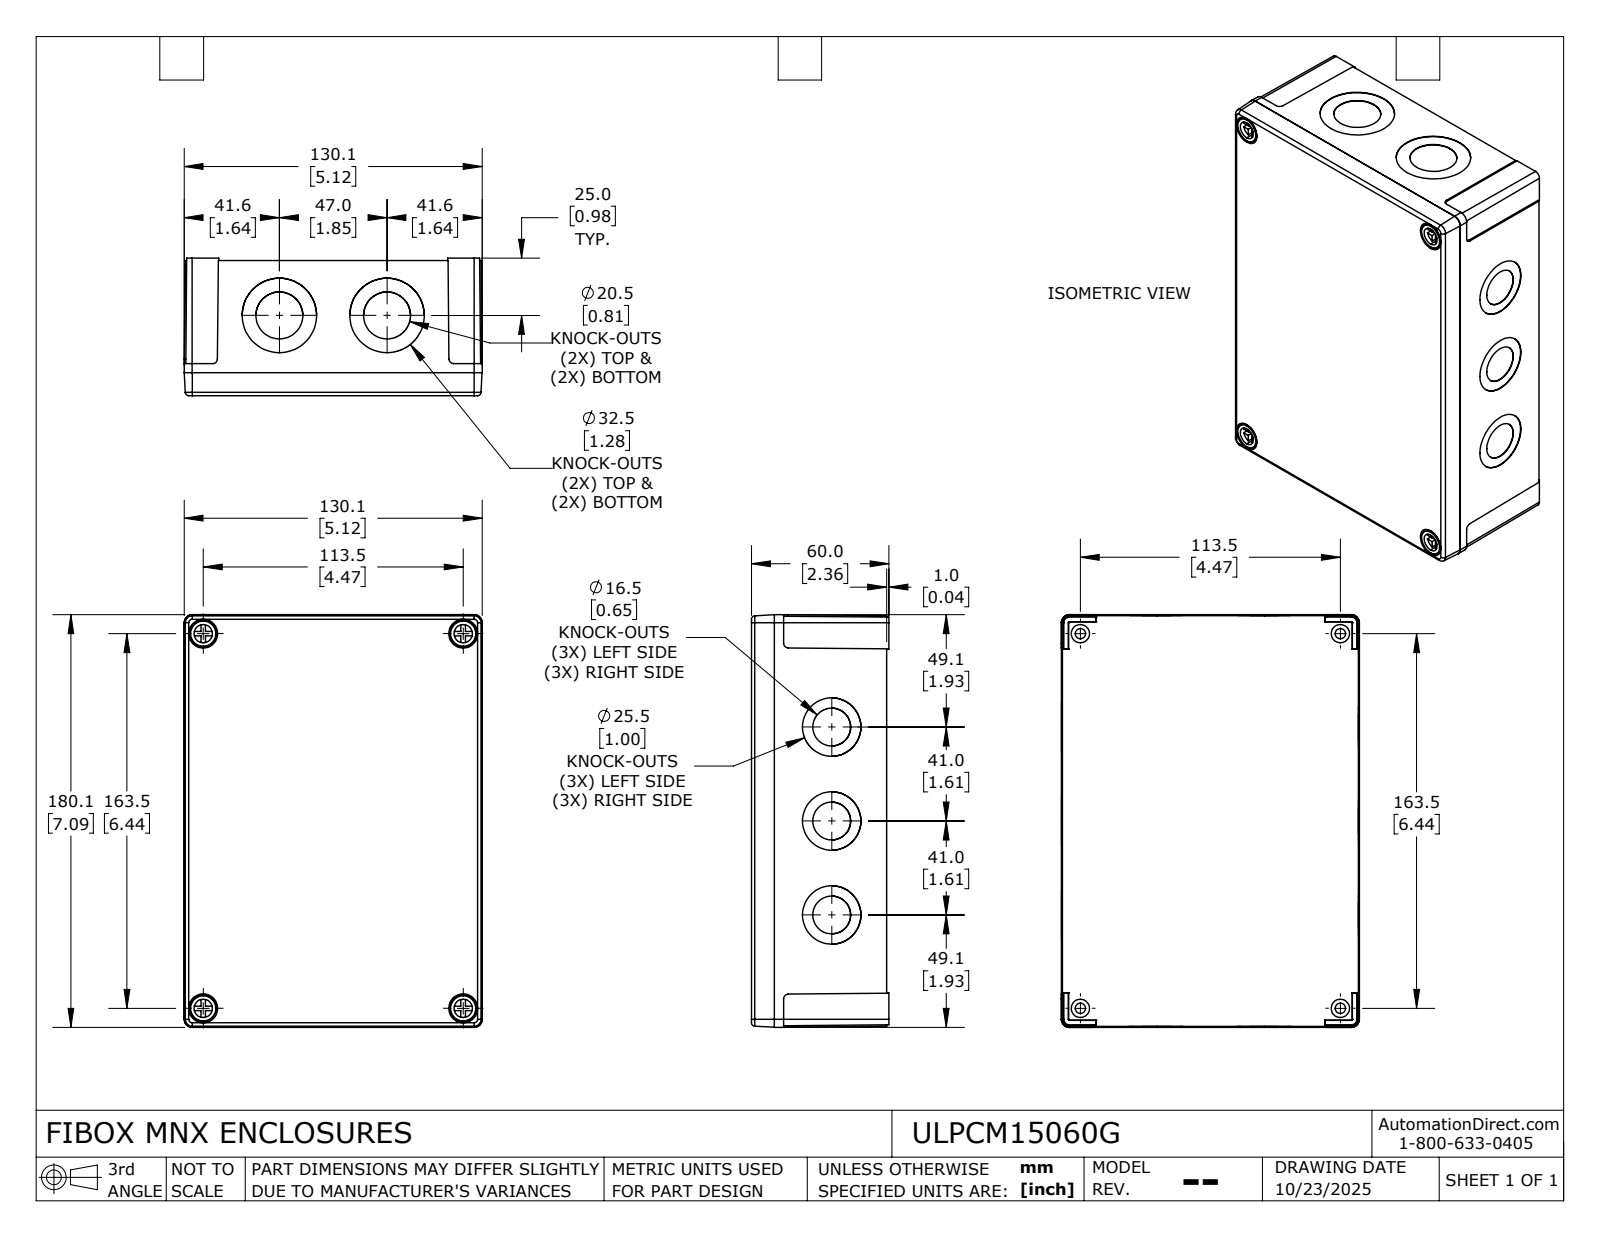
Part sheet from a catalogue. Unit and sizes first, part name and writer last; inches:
Units: inches
Overall size (bounding box): 7.091 × 5.122 × 2.362
Round holes (diameter × count): ⌀0.126 ×8, ⌀0.157 ×8, ⌀0.65 ×6, ⌀1.004 ×6, ⌀0.177 ×4, ⌀0.315 ×4, ⌀0.457 ×4, ⌀0.807 ×4, ⌀1.28 ×4
Round bosses / shafts (diameter × count): ⌀0.315 ×8, ⌀0.098 ×8, ⌀0.433 ×4, ⌀0.283 ×4
Partial cylindrical surfaces — rounded edges, fillets, slot ends (radius × count): R0.039 ×16, R0.056 ×6, R0.021 ×4, R0.059 ×4, R0.079 ×4, R0.197 ×4, R0.023 ×2
Main face-to-face distances: 2.323, 0.126, 2.197, 0.118, 2.205, 2.079, 0.165, 1.929, 0.394, 1.811
Hole centre spacings: 1.333, 1.614, 1.939, 1.969, 2.281, 3.252, 3.276, 4.054
Volume: 18 in³ · Surface area: 266.9 in²
Bodies: 6 solids, 549 faces (285 planar, 212 cylindrical, 52 other)
Part name (STEP PRODUCT): ULPCM15060G_Default
STEP written by: SolidWorks 2024 (CONFIG_CONTROL_DESIGN)
